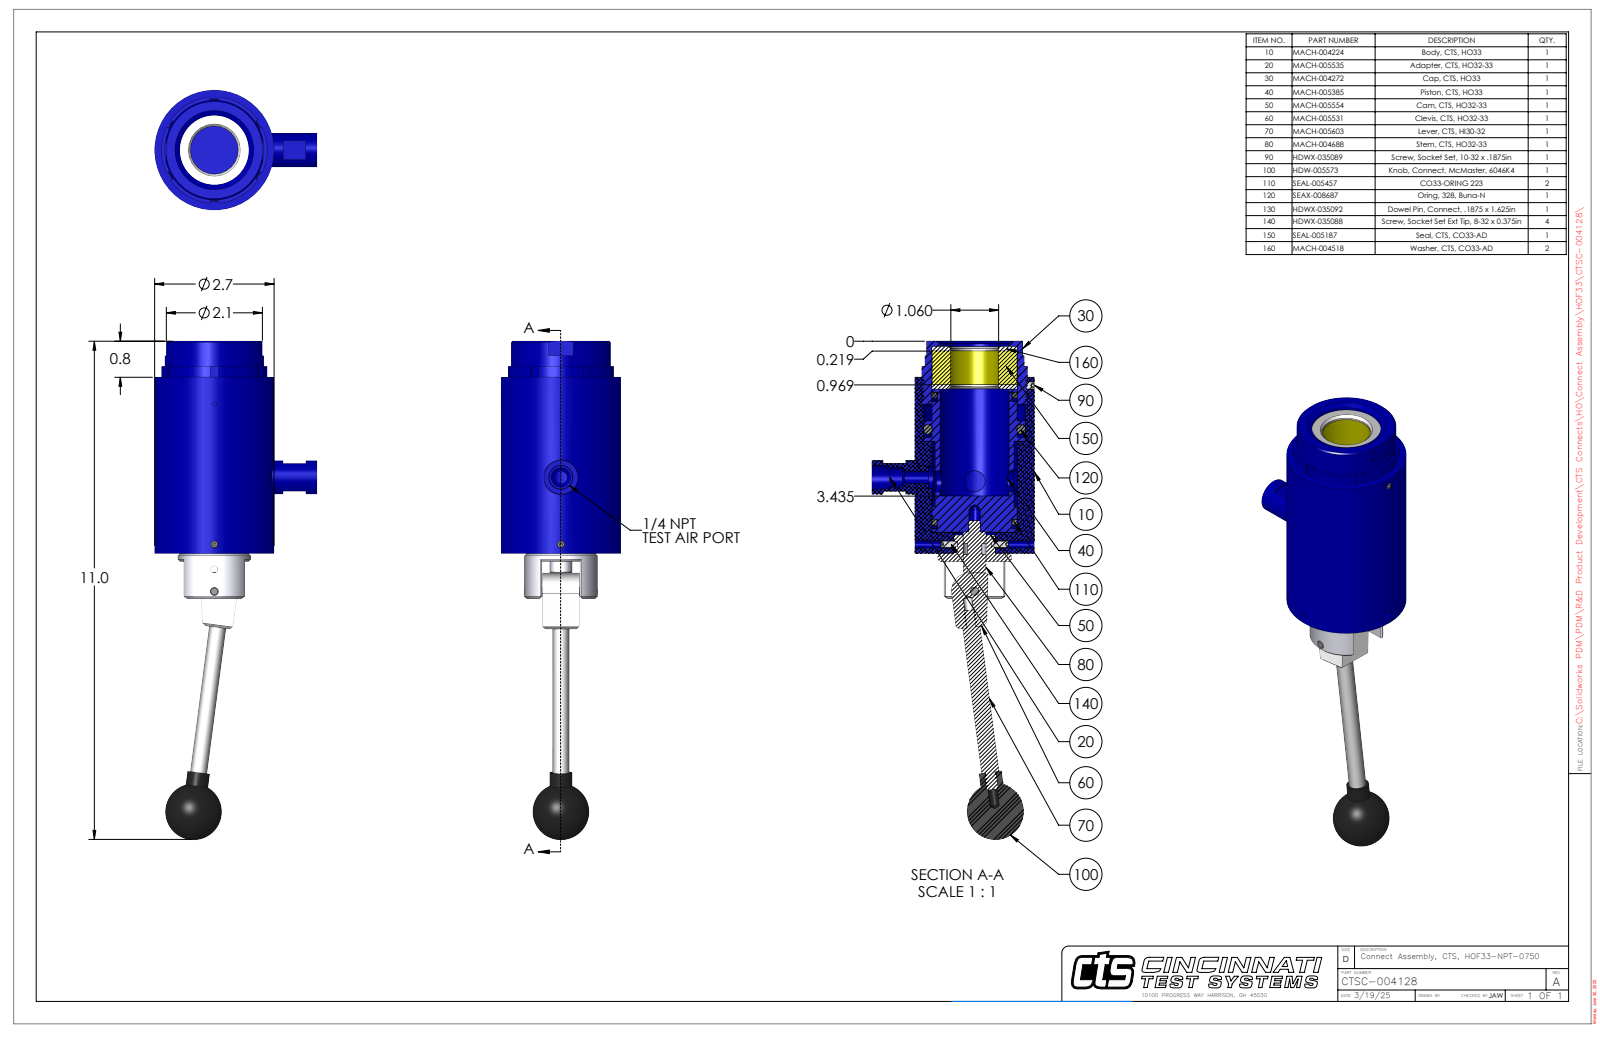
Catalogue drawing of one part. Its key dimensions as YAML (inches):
part_name: "CTSC-004128"
step_written_by: "SolidWorks 2023 (AUTOMOTIVE_DESIGN)"
units: inches
bodies: {solids: 14, faces: 540, planar: 177, cylindrical: 222, other: 141}
overall_size: [11.05, 3.6, 2.65]
volume: 22.22
surface_area: 135.5
round_holes:
  - {diameter: 0.201, count: 3}
  - {diameter: 0.159, count: 2}
  - {diameter: 0.469, count: 2}
  - {diameter: 0.094, count: 1}
  - {diameter: 0.189, count: 1}
  - {diameter: 0.19, count: 1}
  - {diameter: 0.25, count: 1}
  - {diameter: 0.281, count: 1}
  - {diameter: 0.438, count: 1}
  - {diameter: 0.5, count: 1}
  - {diameter: 0.516, count: 1}
  - {diameter: 0.538, count: 1}
round_bosses_or_shafts:
  - {diameter: 0.75, count: 2}
  - {diameter: 0.5, count: 2}
  - {diameter: 0.164, count: 2}
  - {diameter: 0.109, count: 2}
  - {diameter: 2.65, count: 1}
  - {diameter: 2.344, count: 1}
  - {diameter: 2.2, count: 1}
  - {diameter: 1.885, count: 1}
partial_cylinders:
  - {radius: 0.385, count: 1}
  - {radius: 0.4, count: 1}
  - {radius: 1.13, count: 1}
  - {radius: 1.201, count: 1}
face_to_face_distances: [0.844, 0.094, 0.75, 3.739, 4.489, 4.583, 3.645, 0.938, 1.273, 2.372]
hole_center_spacings: [0.089, 0.488, 1.71, 1.948, 2.033, 2.122, 2.436, 3.658]
